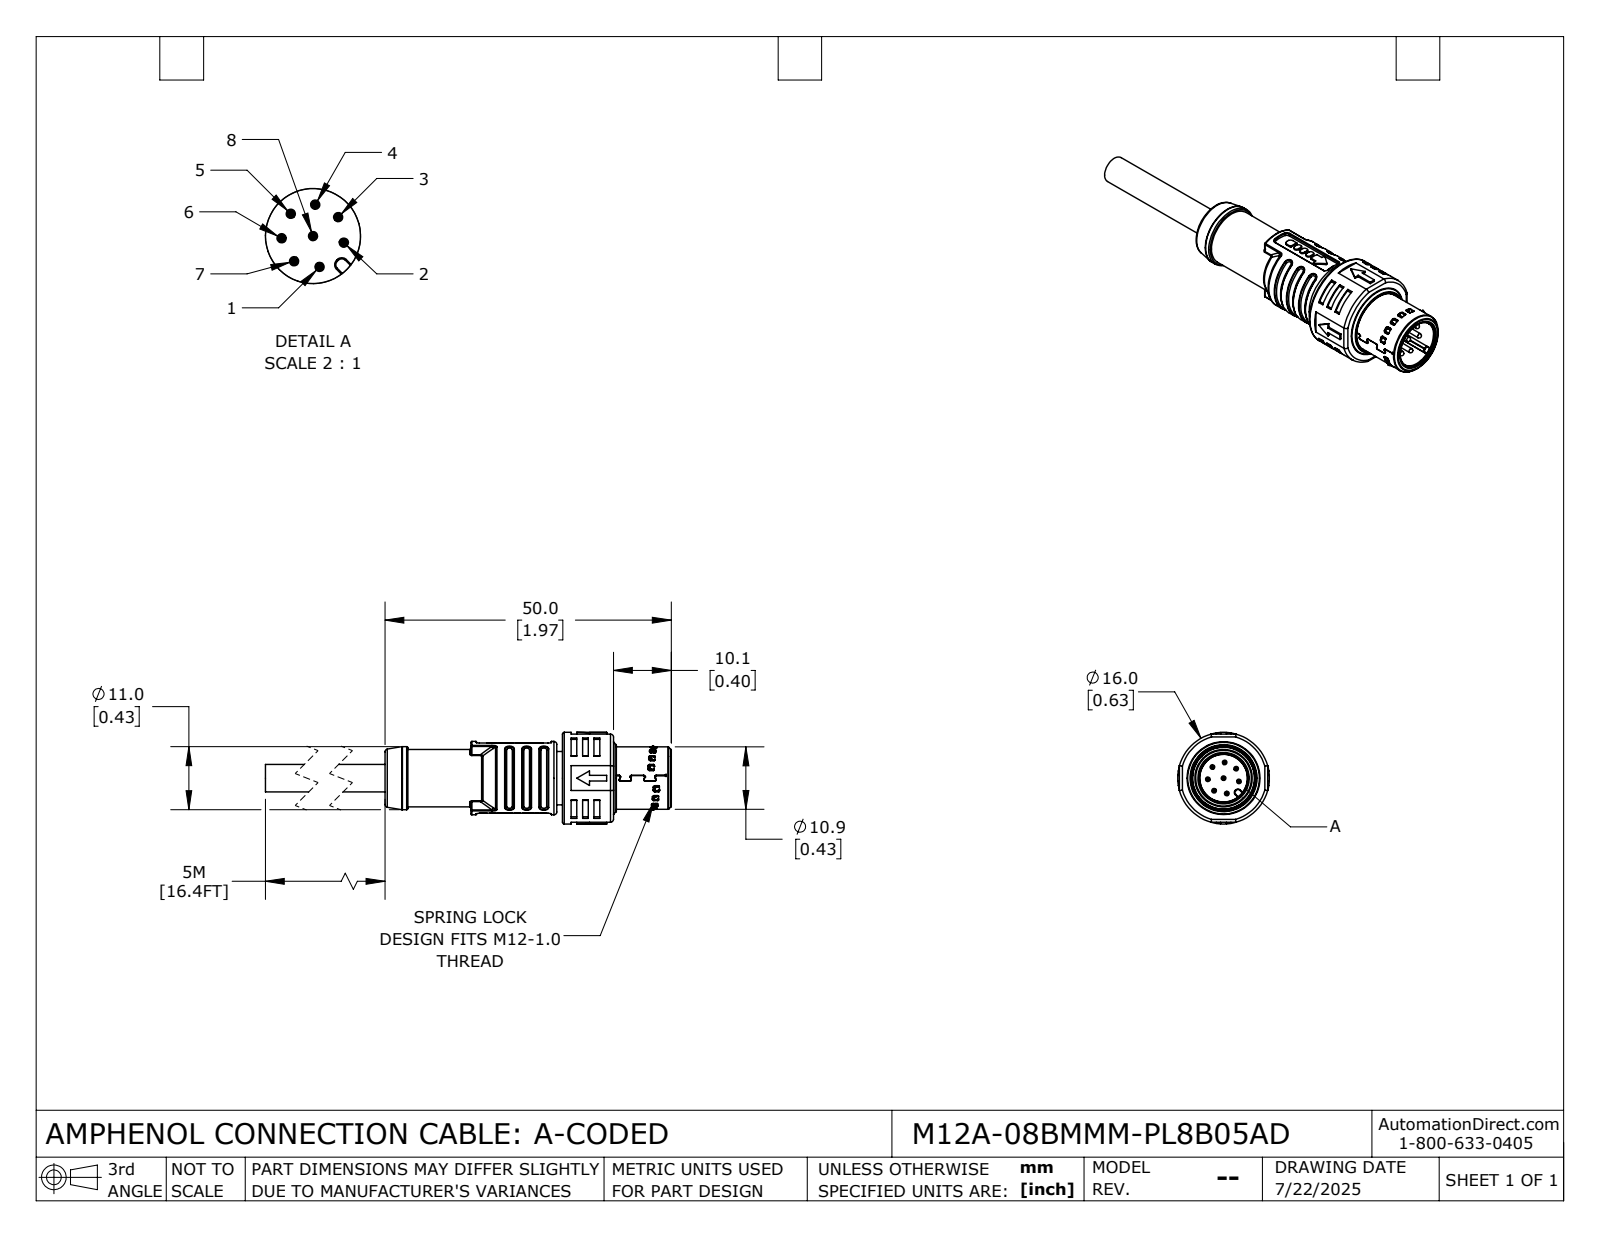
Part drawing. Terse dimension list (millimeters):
name: M12A-08BMMM-PL8B05AD
written by: SolidWorks 2024 (CONFIG_CONTROL_DESIGN)
unit: mm
bodies: 1 solid, 2027 faces (880 planar, 644 cylindrical, 503 other)
size: 75 × 16 × 16
volume: 5 223 mm³; area: 5 723 mm²
holes: 1× ⌀8.3, 1× ⌀9, 1× ⌀10.15, 1× ⌀10.5, 1× ⌀10.9, 1× ⌀11.5, 1× ⌀11.8, 1× ⌀14.2
bosses: 8× ⌀0.8, 1× ⌀16, 1× ⌀14.1, 1× ⌀12.8, 1× ⌀12.4, 1× ⌀11, 1× ⌀10.45, 1× ⌀10.4
rounds: 114× R0.2, 66× R0.25, 64× R0.3, 44× R0.15, 38× R0.5, 12× R0.13, 11× R0.7, 10× R0.1
face distances: 1, 10.1, 8.6, 8.9, 2.5, 1.5, 1.2, 32.5, 15.4, 41.1
